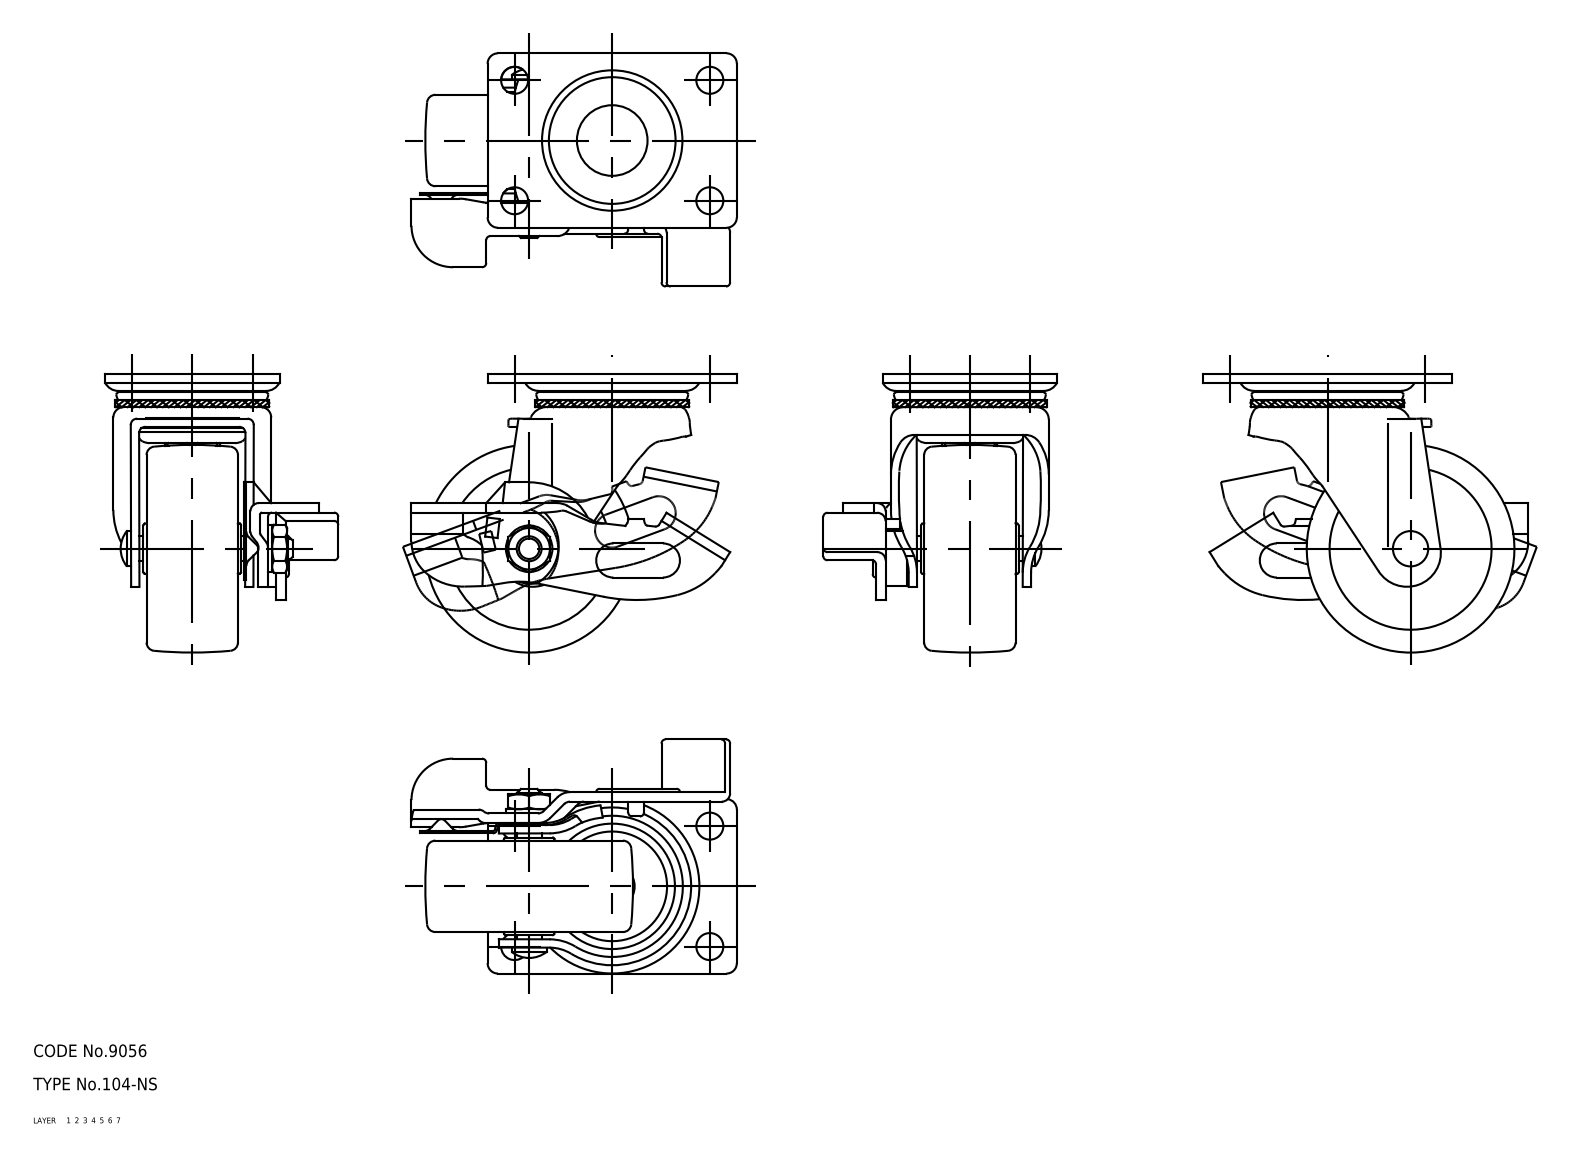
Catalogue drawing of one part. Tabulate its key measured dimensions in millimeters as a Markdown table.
| quantity | value |
| --- | --- |
| part name | plate; wheel; mounting plate; main shaft (+3 more) |
| STEP written by | CADfix (AUTOMOTIVE_DESIGN) |
| units | millimeters |
| bodies | 7 solids, 428 faces (0 planar, 0 cylindrical, 428 other) |
| overall size | 78.33 × 67 × 56.4 |
| volume | 56 732 mm³ |
| surface area | 31 885 mm² |
